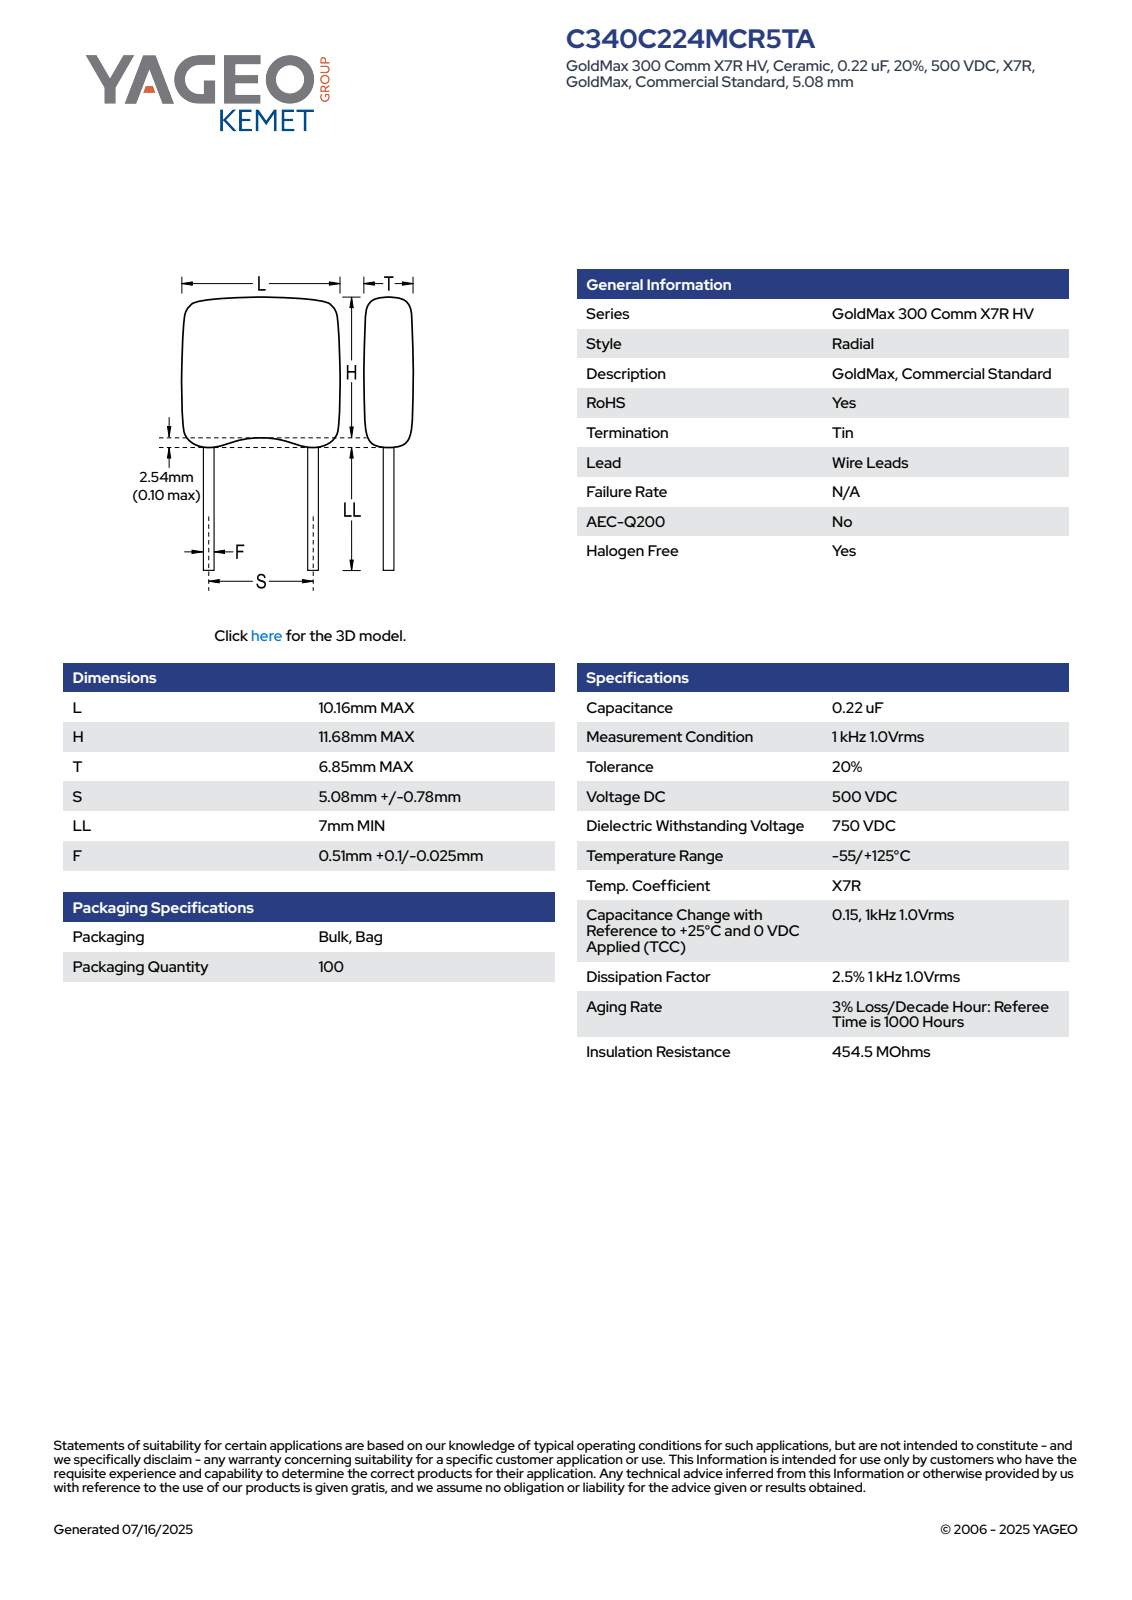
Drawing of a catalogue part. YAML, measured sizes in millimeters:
part_name: "CCR_KRCST2_C340_L10.16H11.68T6.85S5.08LL7F0.61"
step_written_by: "SolidWorks 2014 (AUTOMOTIVE_DESIGN)"
units: millimeters
bodies: {solids: 4, faces: 94, planar: 66, cylindrical: 16, other: 12}
overall_size: [21.22, 10.16, 6.86]
volume: 925
surface_area: 615
round_bosses_or_shafts:
  - {diameter: 0.61, count: 2}
partial_cylinders:
  - {radius: 1, count: 10}
face_to_face_distances: [6.85, 10.16, 14.22, 7, 21.22, 14.95, 7.95, 6.27, 13.56, 6.56]
